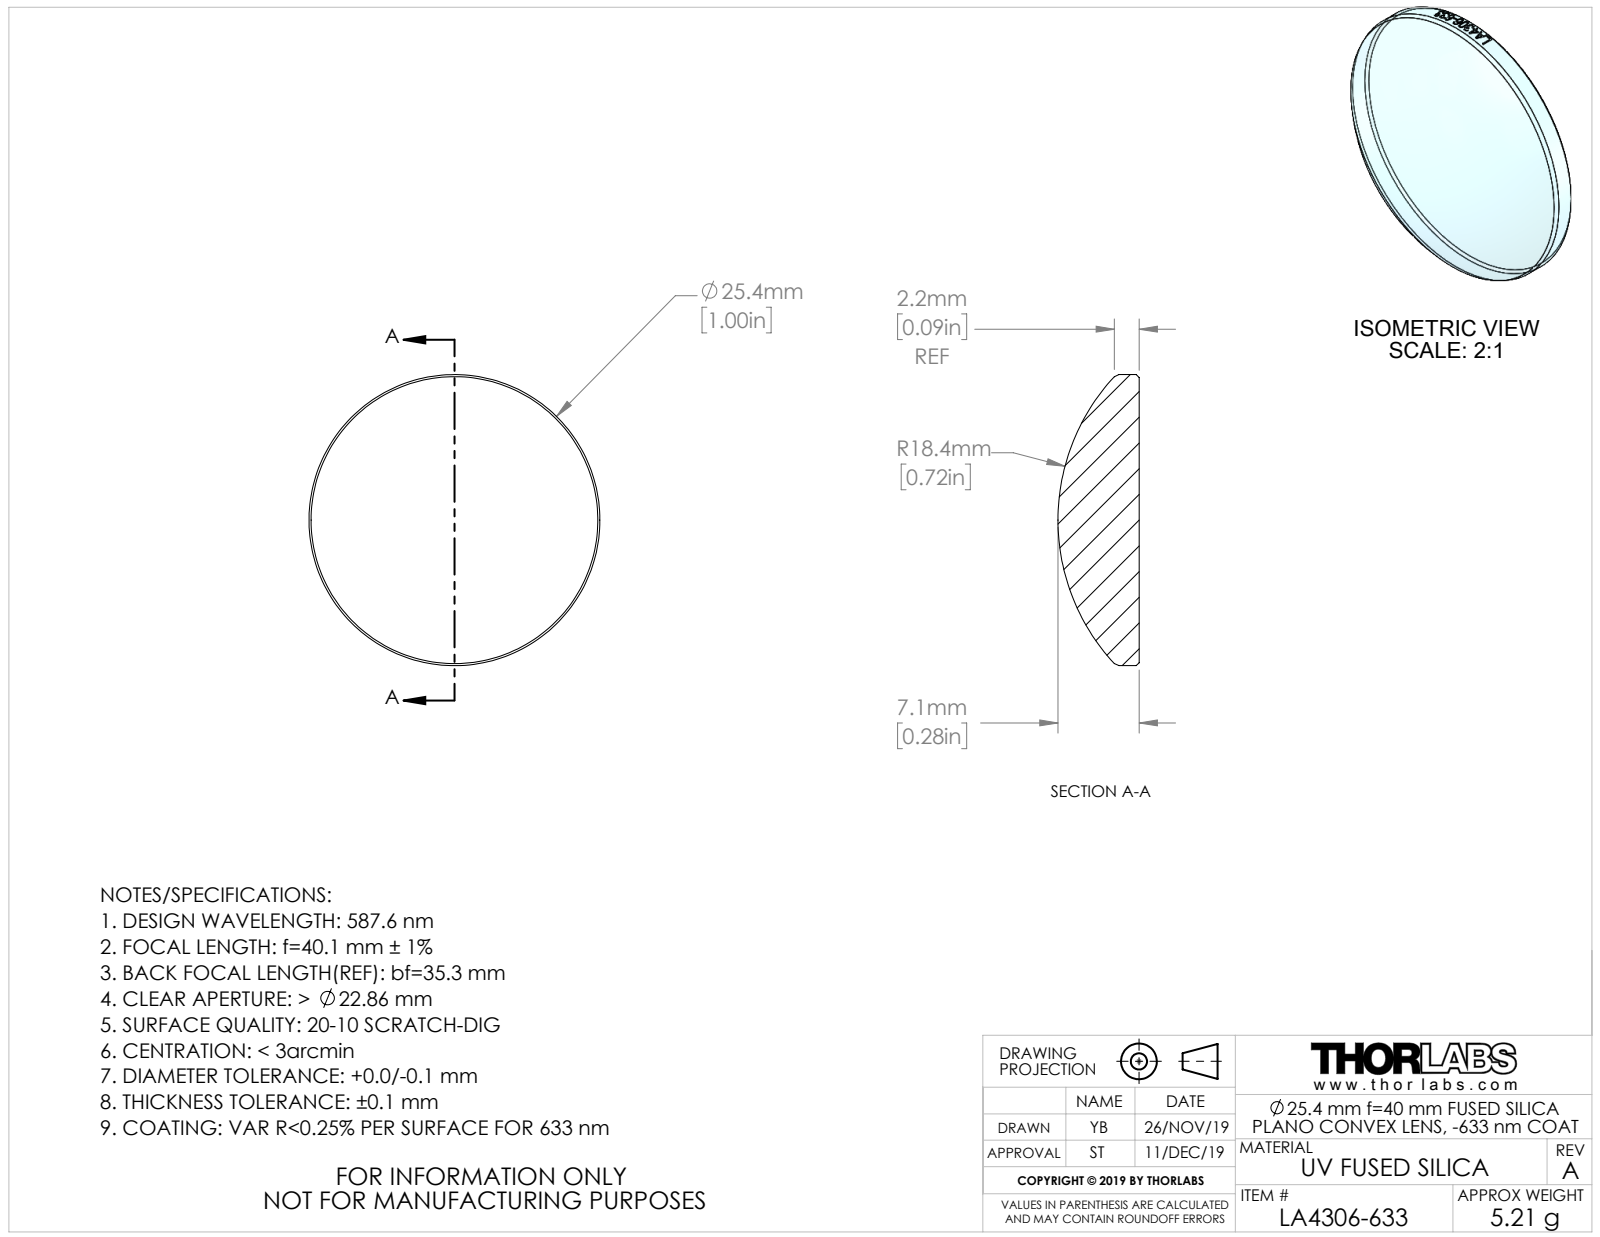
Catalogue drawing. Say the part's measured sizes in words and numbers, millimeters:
The part is named "CTN015013; CTN014994-999". Its 3-D file was written by "SolidWorks 2018 (AUTOMOTIVE_DESIGN)". It is 1 solid with 24 faces: 1 planar, 17 cylindrical and 6 other. Overall it measures 25.4 by 25.4 by 7.08 millimeters. Its volume is 2 365 cubic millimeters and its surface area 1 239 square millimeters. Round bosses or shafts: 1 of diameter 25.4.
